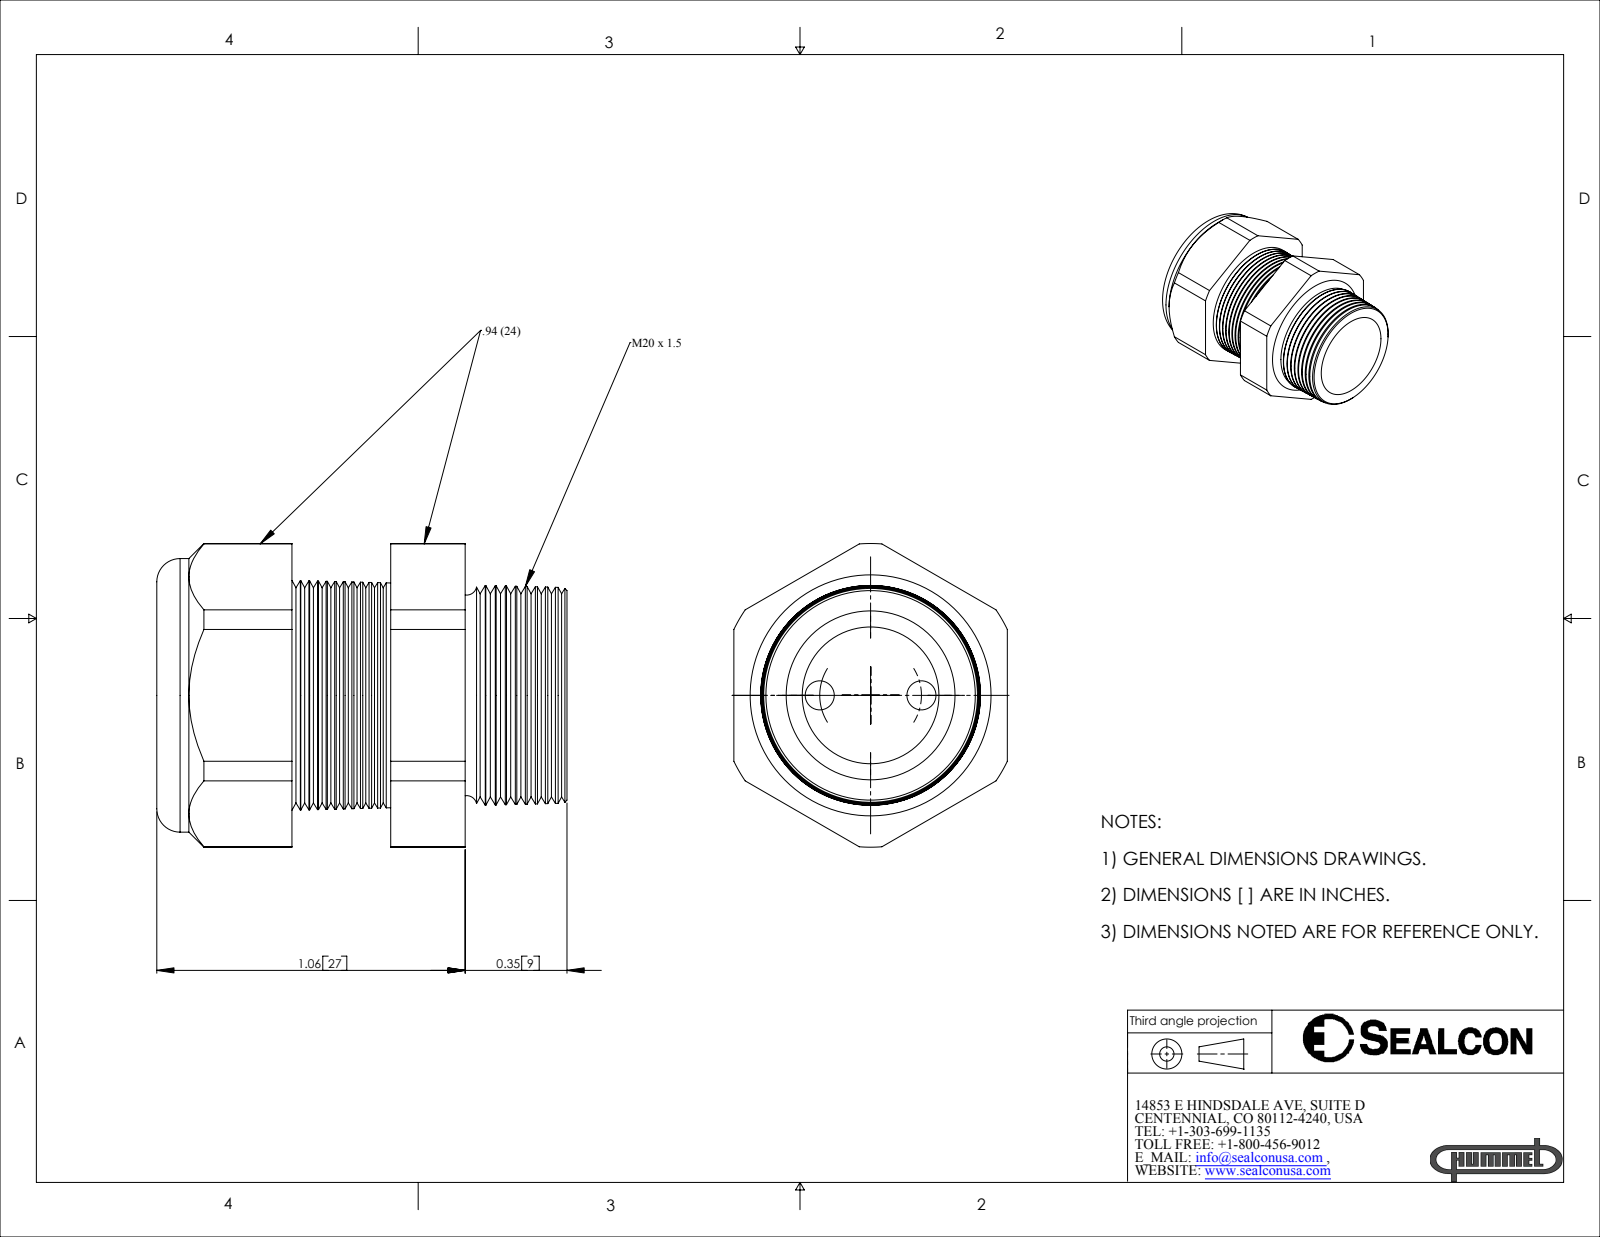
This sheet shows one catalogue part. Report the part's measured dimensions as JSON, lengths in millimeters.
{"part_name": "CD20M9-BK", "step_written_by": "SolidWorks 2007 (CONFIG_CONTROL_DESIGN)", "units": "millimeters", "bodies": {"solids": 2, "faces": 178, "planar": 20, "cylindrical": 24, "other": 134}, "overall_size": [35.8, 26.5, 23.9], "volume_mm3": 9540, "surface_area_mm2": 6357, "round_holes": [[2.5, 2], [11.4, 1], [11.9, 1]], "round_bosses_or_shafts": [[23.9, 1]], "partial_cylinders_radius": [[13.3, 1]], "face_to_face_distances": [23.9, 20.4, 11.8, 8.6, 26.9, 15.1, 6.5, 6.4, 5.5, 14.1], "hole_center_spacings": [4.4, 8.9]}
